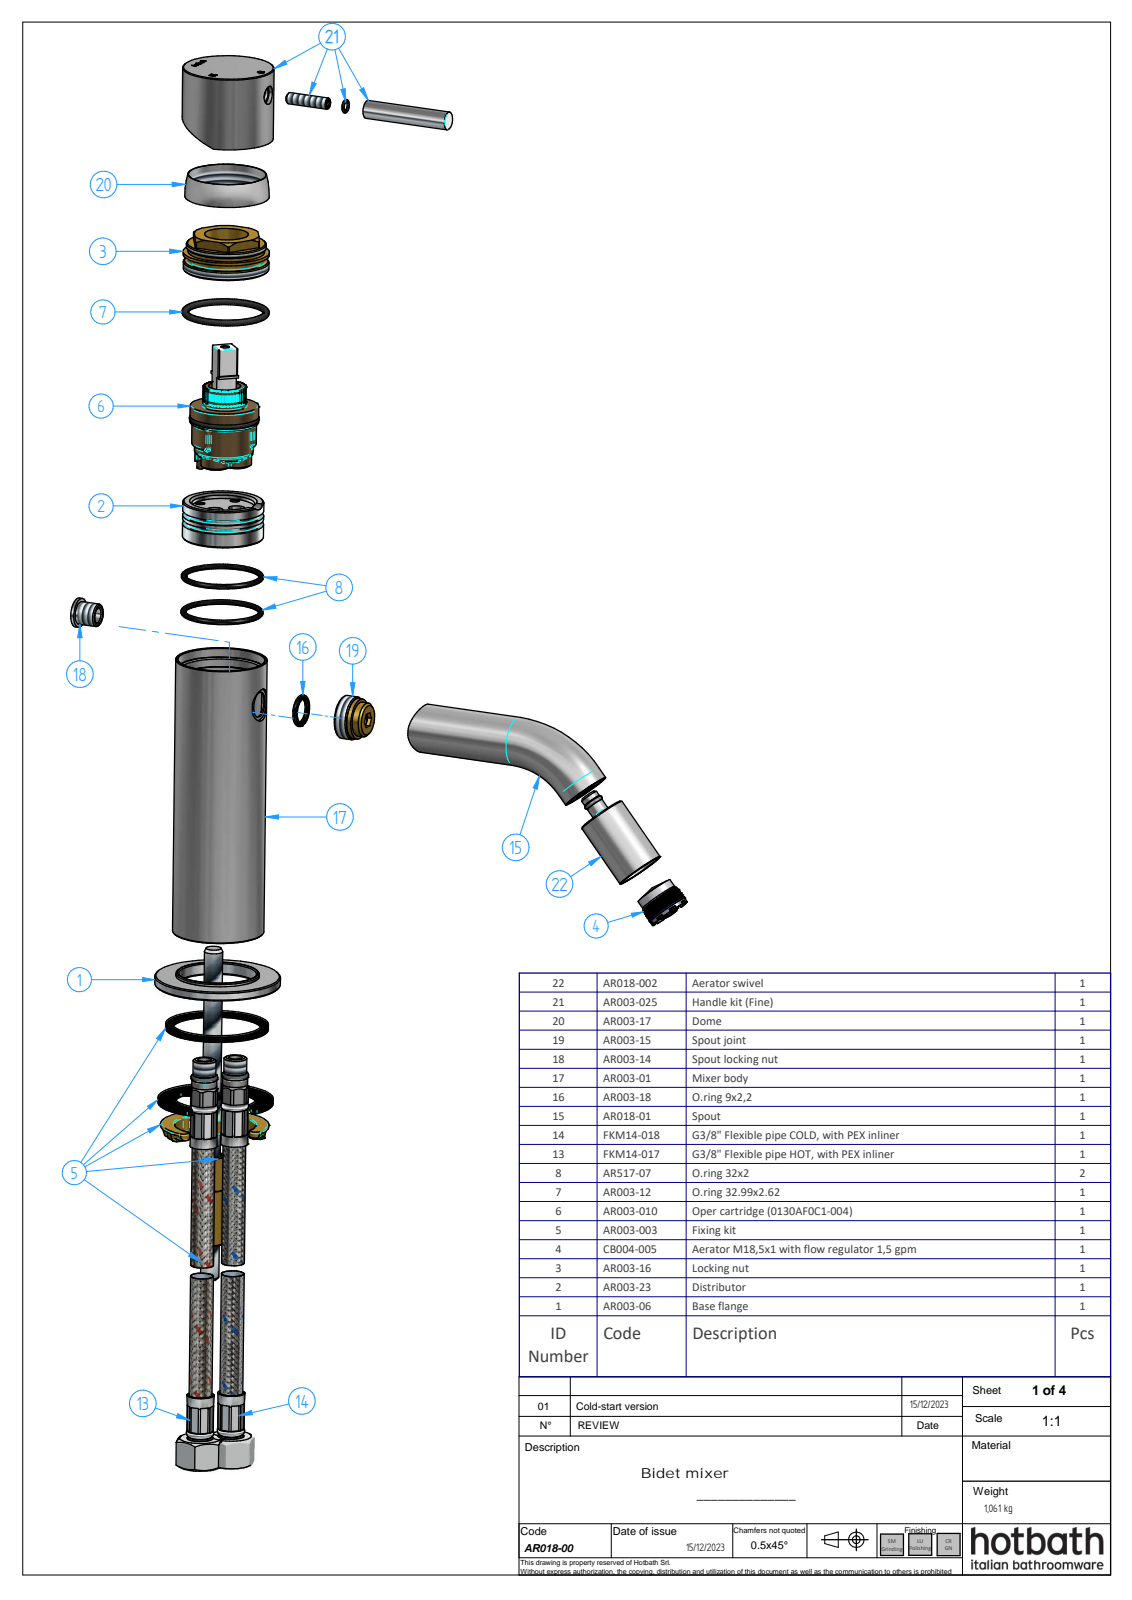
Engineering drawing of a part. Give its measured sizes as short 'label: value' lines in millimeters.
name: AR018-00 rel1; AR003-06; AR003-025_oa_0; AR003-04 (+8 more)
written by: Solid Edge (AUTOMOTIVE_DESIGN)
unit: mm
bodies: 10 solids, 1070 faces (675 planar, 315 cylindrical, 80 other)
size: 161.2 × 157.11 × 55
volume: 90 206 mm³; area: 68 276 mm²
holes: 116× ⌀0.75, 1× ⌀4.13, 1× ⌀4.3, 1× ⌀7, 1× ⌀8, 1× ⌀9, 1× ⌀9.5, 1× ⌀11, 1× ⌀12.5, 1× ⌀13.5, 1× ⌀13.8, 1× ⌀14.1
bosses: 3× ⌀21.3, 2× ⌀40, 2× ⌀18.5, 1× ⌀55, 1× ⌀39, 1× ⌀37.5, 1× ⌀36.85, 1× ⌀36.5
rounds: 4× R0.1, 4× R1.5, 2× R0.24, 2× R0.39, 2× R0.44, 2× R0.69, 1× R0.62, 1× R0.62
face distances: 157.2, 16, 141.2, 4, 145.2, 161.2, 2.2, 1.8, 143, 159
hole spacings: 3.07, 3.08, 3.85, 0.89, 1.17, 2.8, 3.04, 3.17
